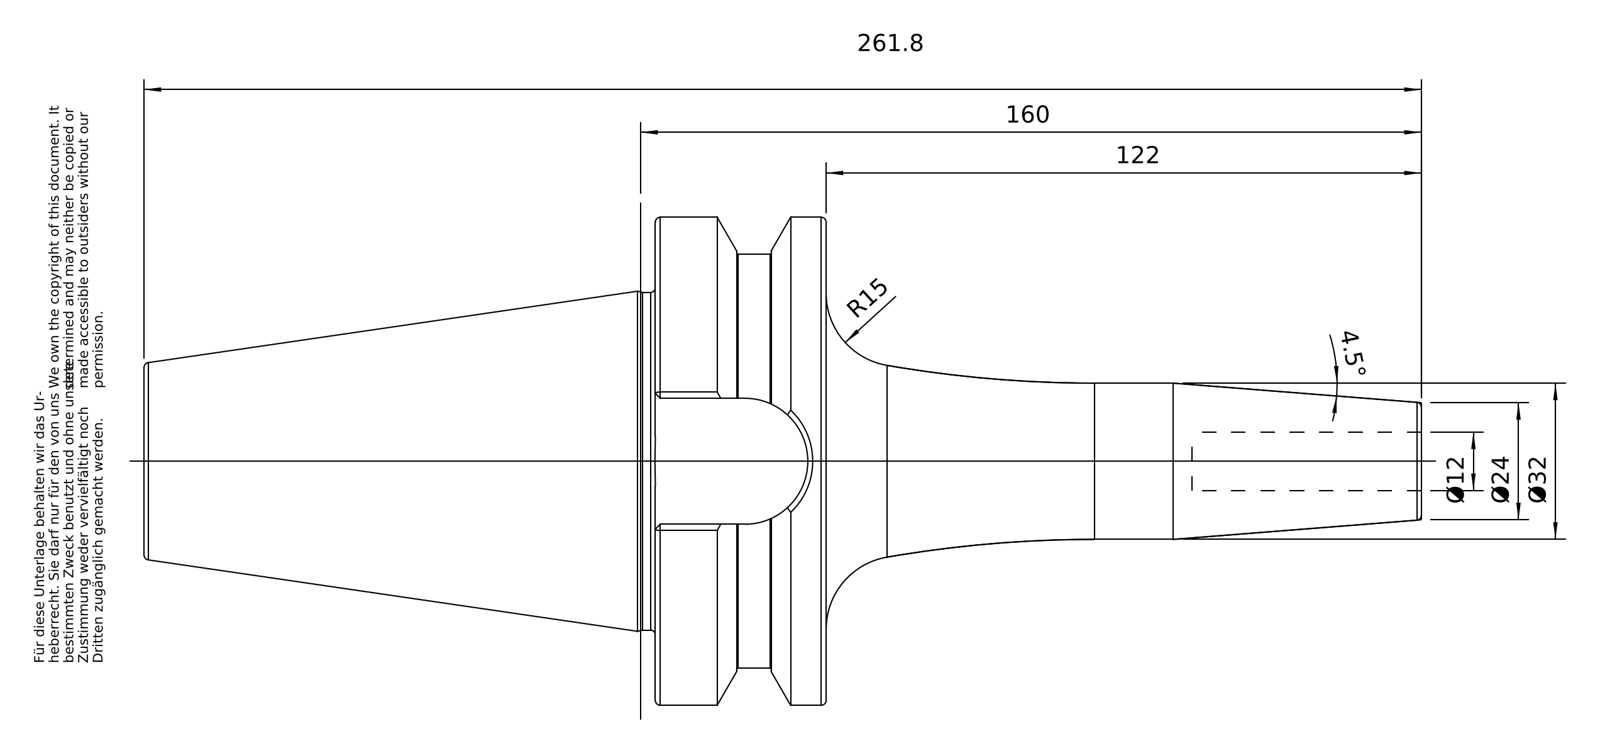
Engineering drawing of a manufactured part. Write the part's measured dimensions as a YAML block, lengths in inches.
part_name: "50-642-12"
step_written_by: "PRO/ENGINEER BY PARAMETRIC TECHNOLOGY CORPORATION, 2010430 (CONFIG_CONTROL_DESIGN)"
units: inches
bodies: {solids: 1, faces: 98, planar: 26, cylindrical: 22, other: 50}
overall_size: [10.307, 3.936, 3.936]
volume: 34.7
surface_area: 99.86
round_holes:
  - {diameter: 0.472, count: 1}
  - {diameter: 0.817, count: 1}
  - {diameter: 0.985, count: 1}
  - {diameter: 1.012, count: 1}
round_bosses_or_shafts:
  - {diameter: 3.936, count: 1}
  - {diameter: 3.337, count: 1}
  - {diameter: 2.722, count: 1}
  - {diameter: 1.26, count: 1}
  - {diameter: 0.945, count: 1}
partial_cylinders:
  - {radius: 0.508, count: 1}
face_to_face_distances: [1.378, 2.772, 4.126, 5.504, 1.016, 10.307, 6.181, 4.803, 1.89, 2.236]
